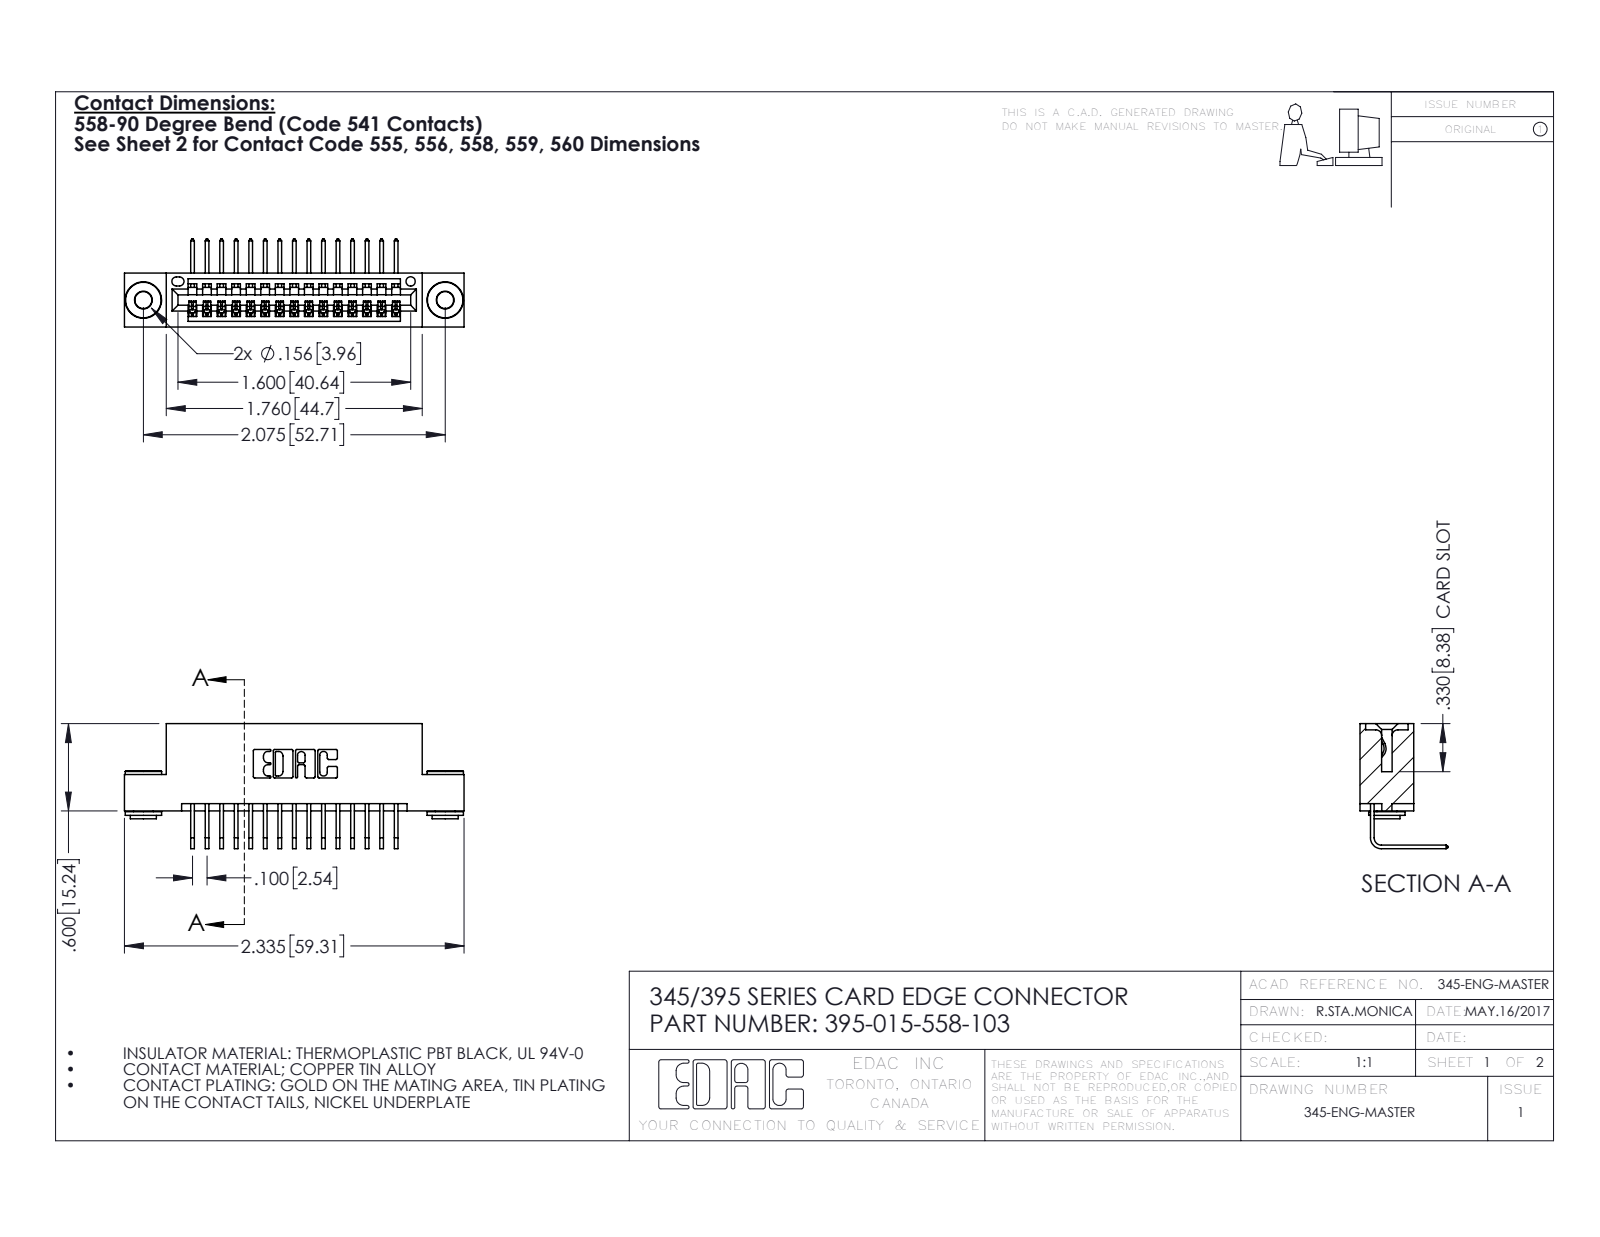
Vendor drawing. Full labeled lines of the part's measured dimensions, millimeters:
Part name (STEP PRODUCT): 345-292-001_558 Tail - 2; 395-015-558-103; 345 Part_Flush Mounting Lugs - 0.156 Dia-TH; 345-250-002_345-250-002-102
STEP written by: SolidWorks 2016 (CONFIG_CONTROL_DESIGN)
Units: millimetres
Bodies: 18 solids, 1064 faces (720 planar, 336 cylindrical, 8 other)
Overall size (bounding box): 59.3 × 21.8 × 15.4
Volume: 5 470 mm³ · Surface area: 7 426 mm²
Round holes (diameter × count): ⌀2.9 ×2, ⌀4 ×2, ⌀1.6 ×1
Round bosses / shafts (diameter × count): ⌀6.4 ×2, ⌀4.6 ×2, ⌀3.5 ×2
Partial cylindrical surfaces — rounded edges, fillets, slot ends (radius × count): R0.2 ×30, R0.3 ×22, R0.2 ×6, R0.8 ×6, R0.7 ×3, R0.8 ×2, R1 ×2, R0.4 ×1
Main face-to-face distances: 5.1, 1.8, 7.6, 9.4, 0.6, 2.5, 6.9, 5.7, 2.5, 15.2
Hole centre spacings: 6.9, 46.8, 52.7
